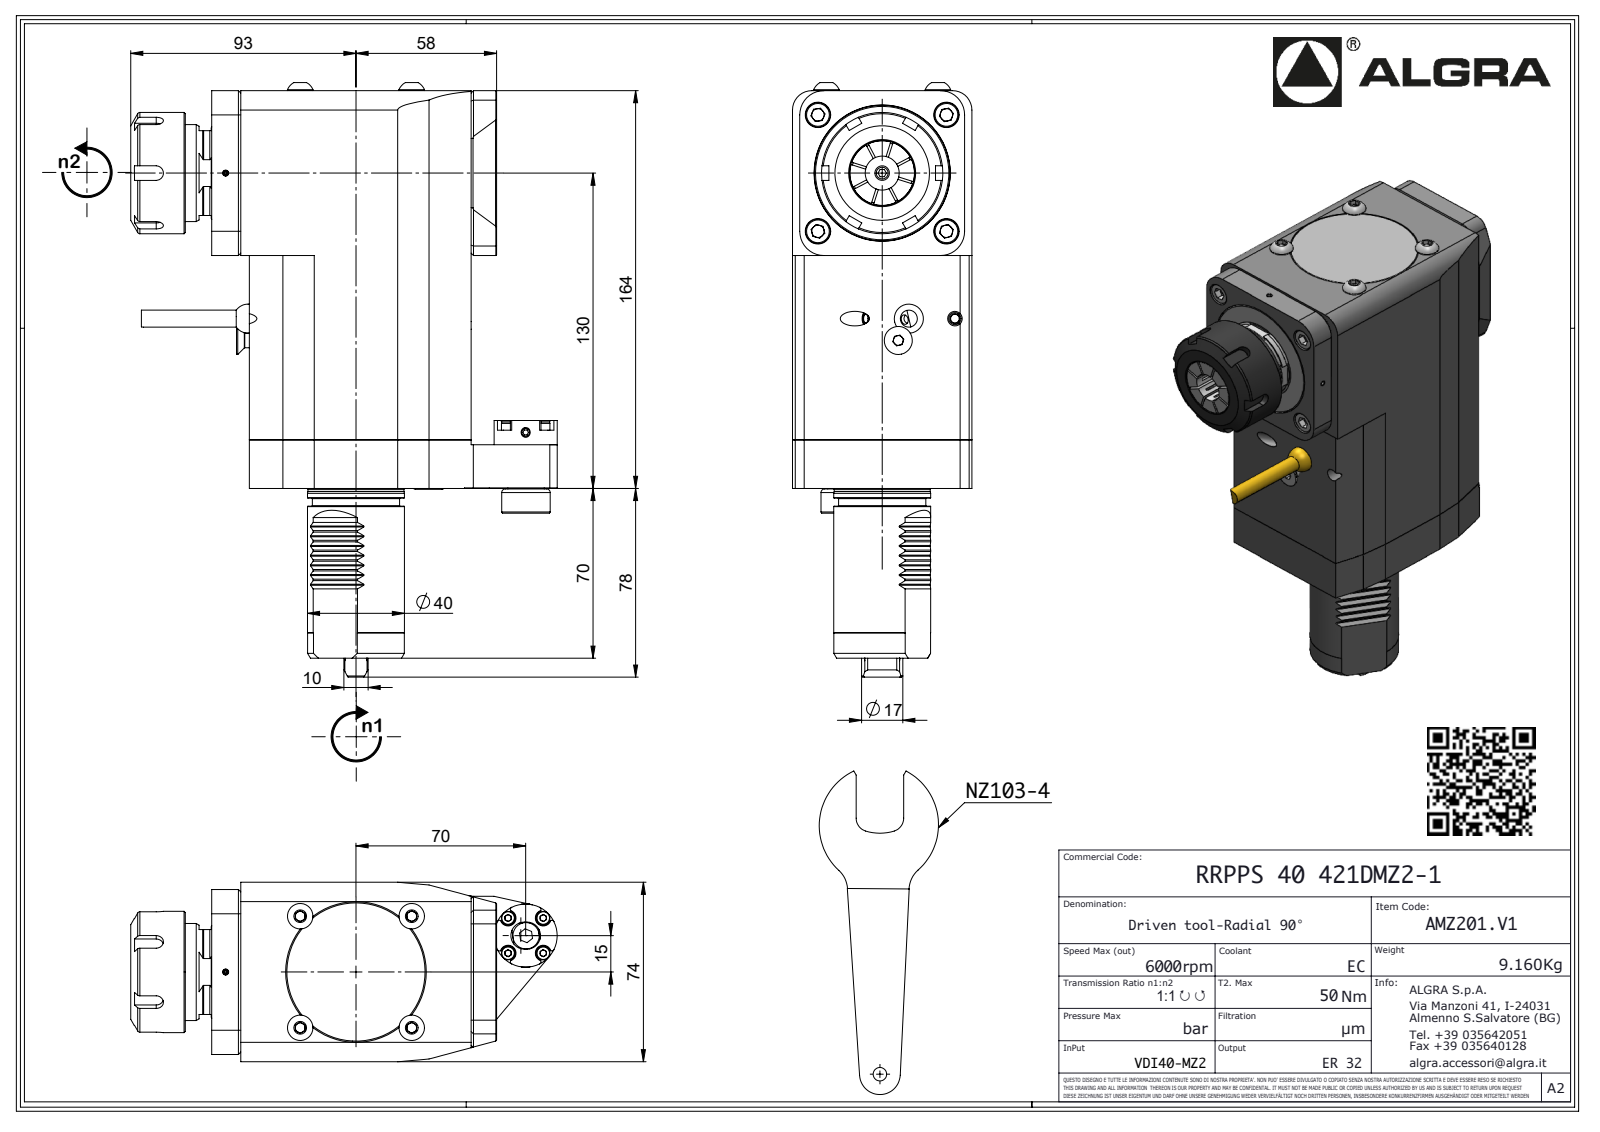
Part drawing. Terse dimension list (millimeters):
name: RRPPS40421DMZ2-1
written by: SolidWorks 2016 (AUTOMOTIVE_DESIGN)
unit: mm
bodies: 1 solid, 561 faces (375 planar, 70 cylindrical, 116 other)
size: 241.8 × 174.03 × 74
volume: 1 343 000 mm³; area: 92 452 mm²
holes: 1× ⌀4, 1× ⌀4.2
bosses: 1× ⌀41.5, 1× ⌀40, 1× ⌀39.9, 1× ⌀39.6, 1× ⌀36, 1× ⌀32, 1× ⌀26, 1× ⌀20
rounds: 7× R0.3, 7× R0.67, 7× R1.04, 7× R7.41, 4× R6, 4× R10, 3× R3, 3× R8
face distances: 74, 164, 91.5, 15.5, 107, 117.5, 102, 10.5, 76.7, 68
